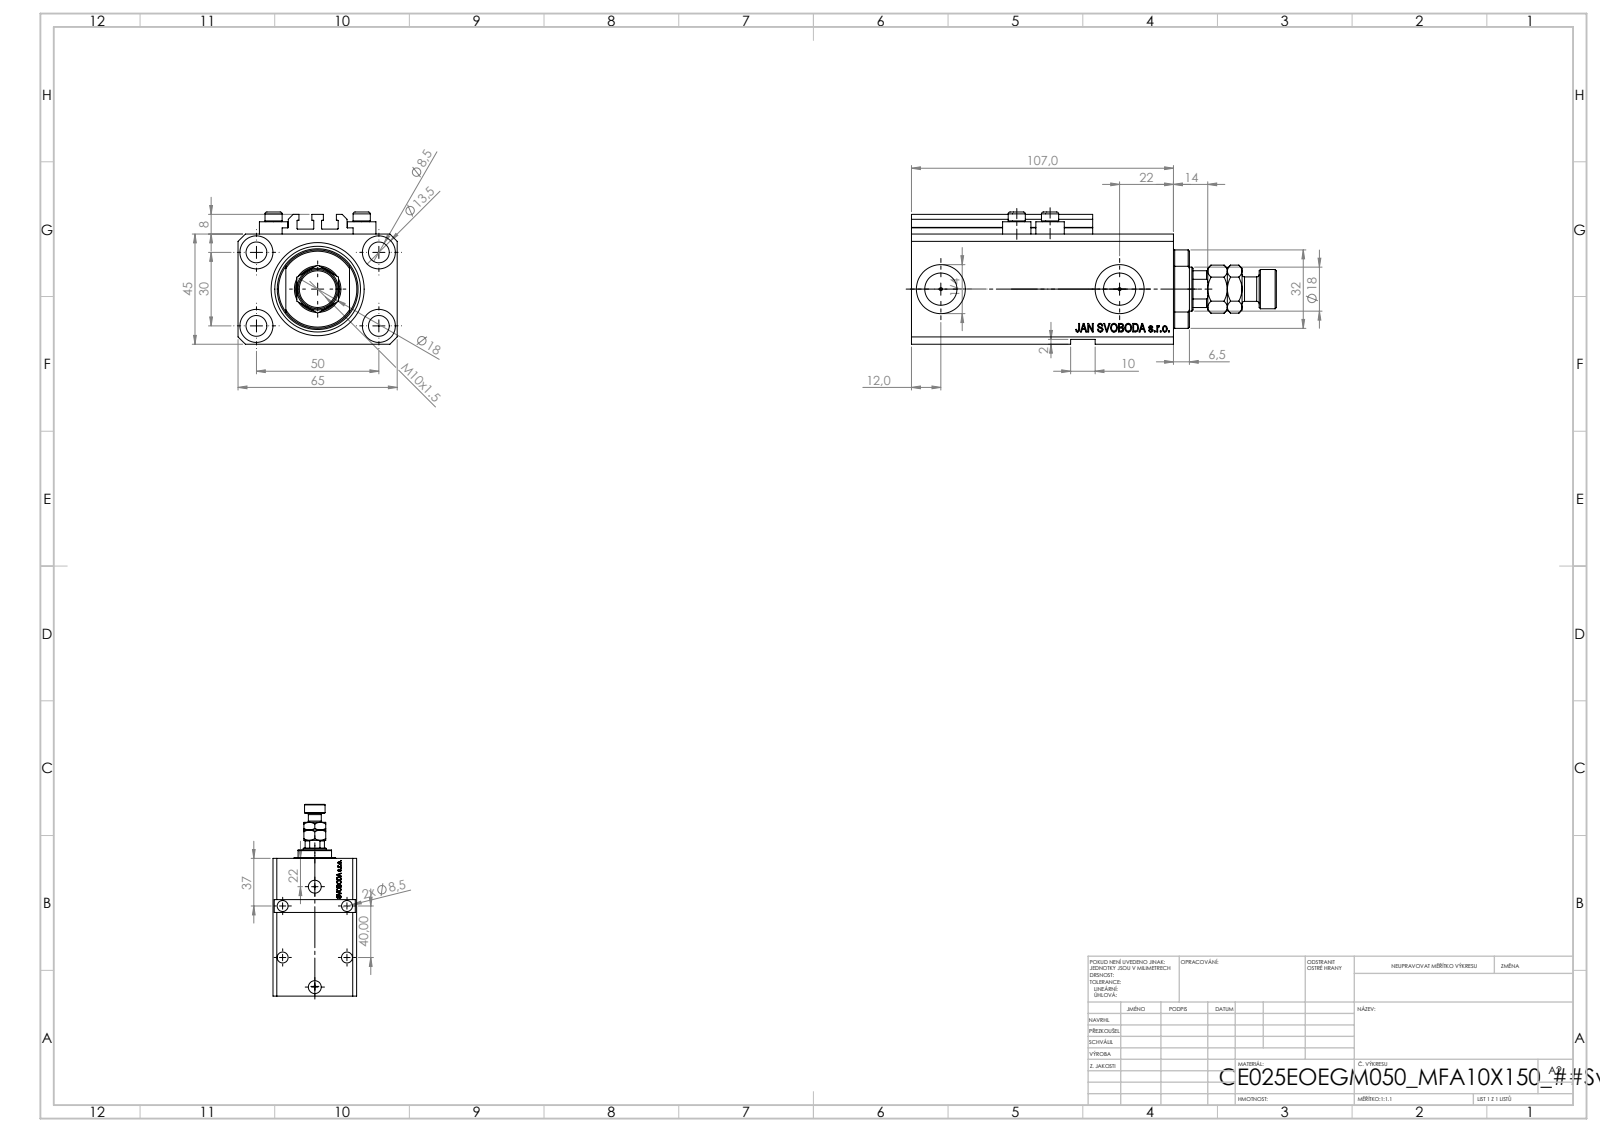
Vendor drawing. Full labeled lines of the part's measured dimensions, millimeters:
Part name (STEP PRODUCT): V250CE_C_VCP; ALLEN BOLT V250CE; V250CE_VC_E; V250CE_E_Body (+1 more)
STEP written by: SolidWorks 2019 (CONFIG_CONTROL_DESIGN)
Units: millimetres
Bodies: 9 solids, 1139 faces (527 planar, 150 cylindrical, 462 other)
Overall size (bounding box): 149 × 65 × 54
Volume: 278 825 mm³ · Surface area: 78 940 mm²
Round holes (diameter × count): ⌀8.5 ×9, ⌀1.25 ×4, ⌀4 ×4, ⌀13.5 ×4, ⌀10 ×2, ⌀13.16 ×2, ⌀20 ×2, ⌀18 ×1, ⌀25 ×1, ⌀38 ×1
Round bosses / shafts (diameter × count): ⌀11.6 ×4, ⌀7 ×4, ⌀16 ×1, ⌀10 ×1
Partial cylindrical surfaces — rounded edges, fillets, slot ends (radius × count): R0.2 ×10, R8.5 ×1, R16 ×1
Main face-to-face distances: 45, 65, 14, 93, 2, 47, 107, 6.9, 20.5, 2.5
Hole centre spacings: 29.15, 50, 13.6, 14.76, 15.12, 27.51, 27.89, 30
